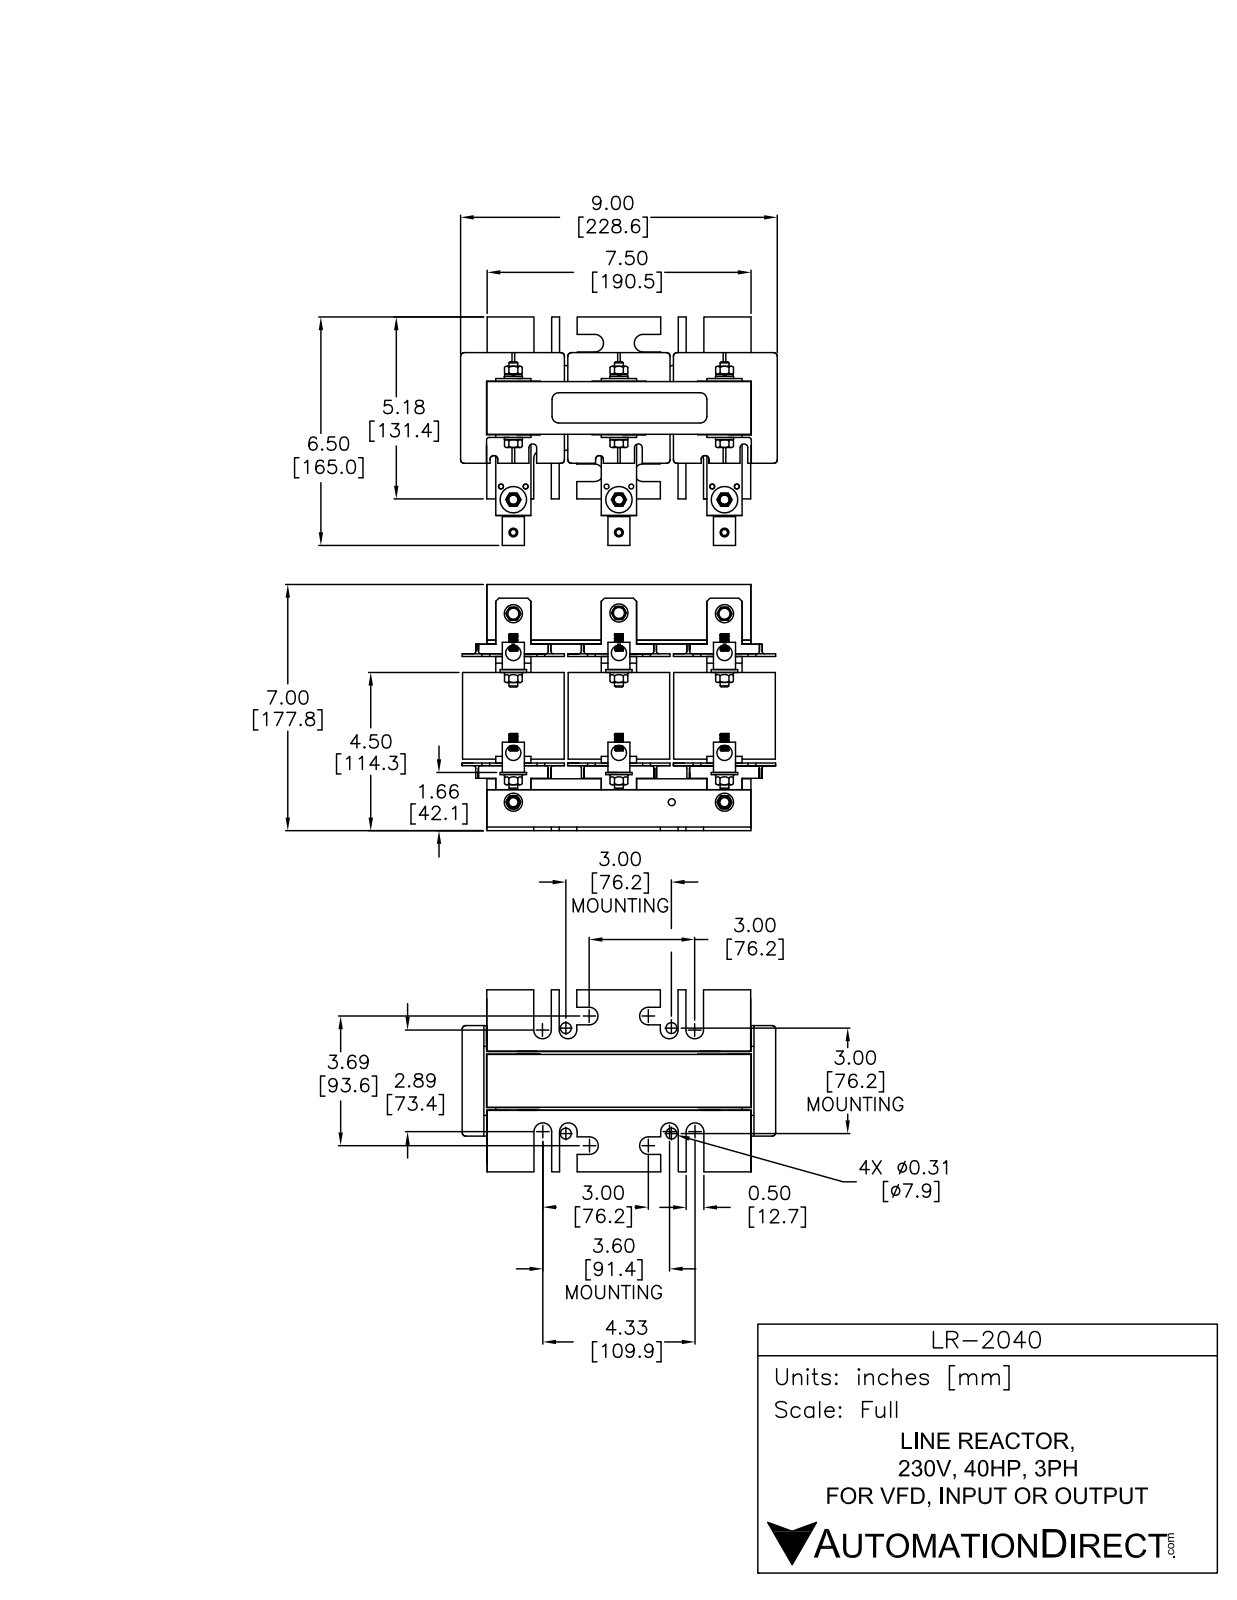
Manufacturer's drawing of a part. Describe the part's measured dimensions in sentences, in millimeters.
The part is named "LR-2040". Its 3-D file was written by "SolidWorks 2011 (AUTOMOTIVE_DESIGN)". It is 47 solids with 972 faces: 716 planar, 244 cylindrical and 12 other. Overall it measures 227 by 177.7 by 160.75 millimeters. Its volume is 2 667 000 cubic millimeters and its surface area 555 030 square millimeters. Round holes: 6 of diameter 10.75, 3 of diameter 11.5, 3 of diameter 11.51. Round bosses or shafts: 11 of diameter 15, 9 of diameter 18.75, 9 of diameter 6, 6 of diameter 10.5, 2 of diameter 6. Partial cylindrical surfaces (rounded edges, fillets, slot ends): 16 of radius 15, 12 of radius 6.35, 12 of radius 7, 6 of radius 2.75, 6 of radius 15.25, 4 of radius 1.5, 3 of radius 23.44, 3 of radius 24. The main face-to-face distances are 76.5, 2, 9, 87.5, 85.5, 7, 78.5, 38, 38.5, 42.5. The hole center spacings are 76.5, 76.84, 104.71, 153, 7.17, 71.5, 153.17, 168.88.
